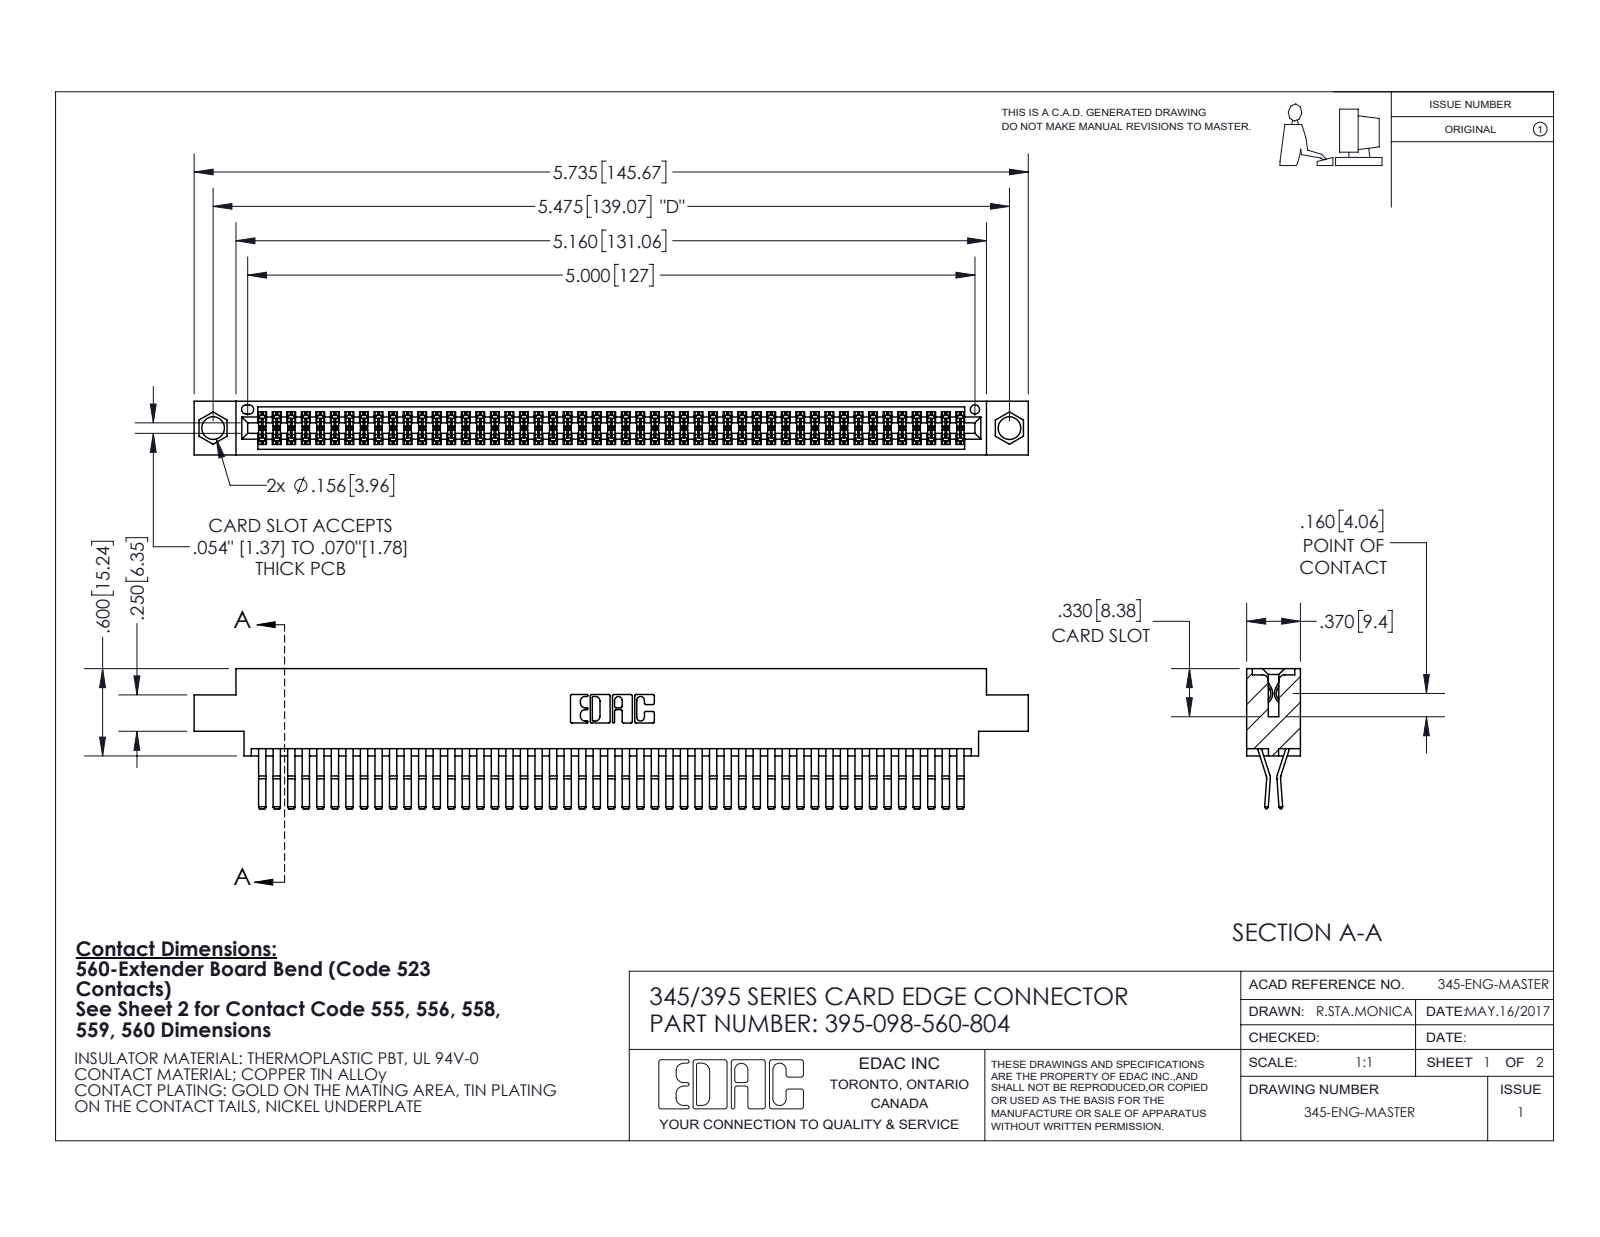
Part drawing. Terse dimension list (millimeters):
name: 345-292-001_560 Tail; 345 Part_0.170 Offset - 0.156 Dia-TI; 395-098-560-804
written by: SolidWorks 2020 (CONFIG_CONTROL_DESIGN)
unit: mm
bodies: 99 solids, 5240 faces (3332 planar, 1908 cylindrical, 0 other)
size: 145.7 × 24.4 × 9.4
volume: 14 600 mm³; area: 23 420 mm²
holes: 2× ⌀4, 1× ⌀1.6
rounds: 196× R0.2, 22× R0.3, 6× R0.2, 6× R0.8, 3× R0.7, 2× R0.3, 2× R0.4, 2× R0.5
face distances: 0.6, 1.8, 7.6, 9.4, 5.1, 2.5, 6.9, 5.7, 4.4, 3.8
hole spacings: 6.9, 133.1, 139.1
